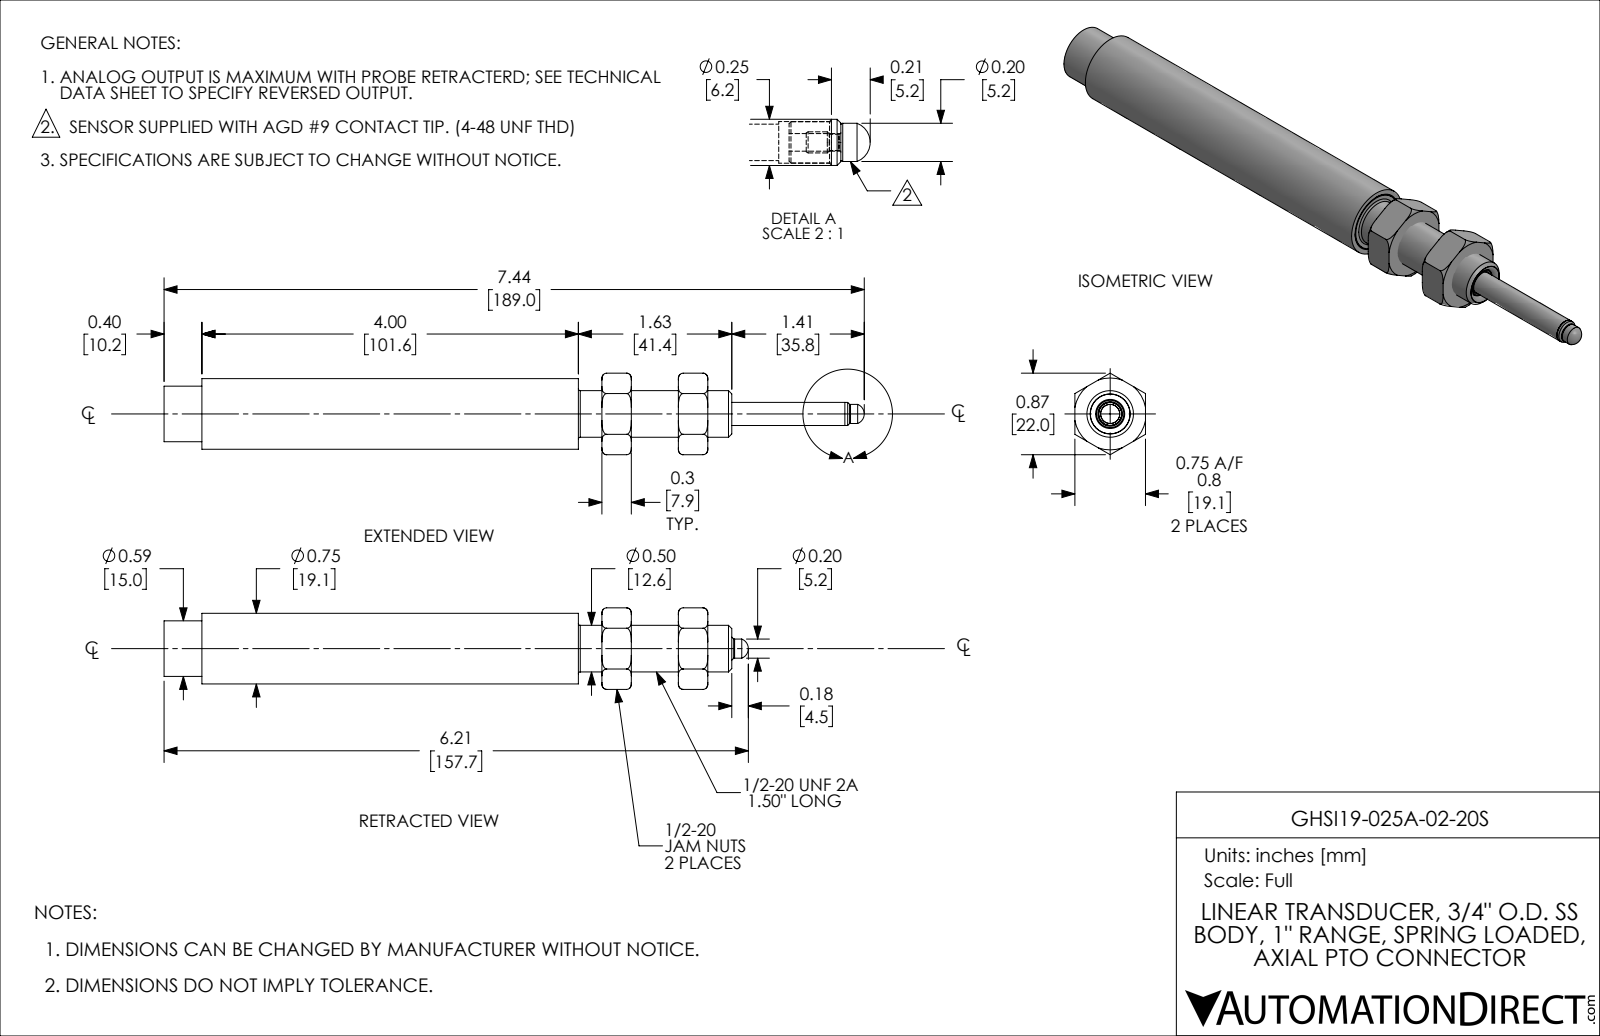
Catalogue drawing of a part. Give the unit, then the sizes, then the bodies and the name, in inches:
Units: inches
Overall size (bounding box): 6.208 × 0.866 × 0.75
Round holes (diameter × count): ⌀0.093 ×1, ⌀0.156 ×1, ⌀0.193 ×1, ⌀0.221 ×1, ⌀0.249 ×1, ⌀0.302 ×1, ⌀0.31 ×1, ⌀0.453 ×1, ⌀0.52 ×1, ⌀0.62 ×1, ⌀0.625 ×1, ⌀0.65 ×1
Round bosses / shafts (diameter × count): ⌀0.03 ×6, ⌀0.75 ×1, ⌀0.725 ×1, ⌀0.672 ×1, ⌀0.624 ×1, ⌀0.59 ×1, ⌀0.495 ×1, ⌀0.375 ×1
Partial cylindrical surfaces — rounded edges, fillets, slot ends (radius × count): R0.011 ×2, R0.04 ×2, R0.133 ×1, R0.156 ×1, R0.275 ×1
Main face-to-face distances: 0.75, 0.812, 0.313, 0.813, 1.125, 0.5, 0.312, 0.75, 4.272, 4.585
Volume: 1.273 in³ · Surface area: 39.45 in²
Bodies: 11 solids, 187 faces (77 planar, 65 cylindrical, 45 other)
Part name (STEP PRODUCT): GHSI19-025A-02-20S
STEP written by: SolidWorks 2019 (AUTOMOTIVE_DESIGN)
